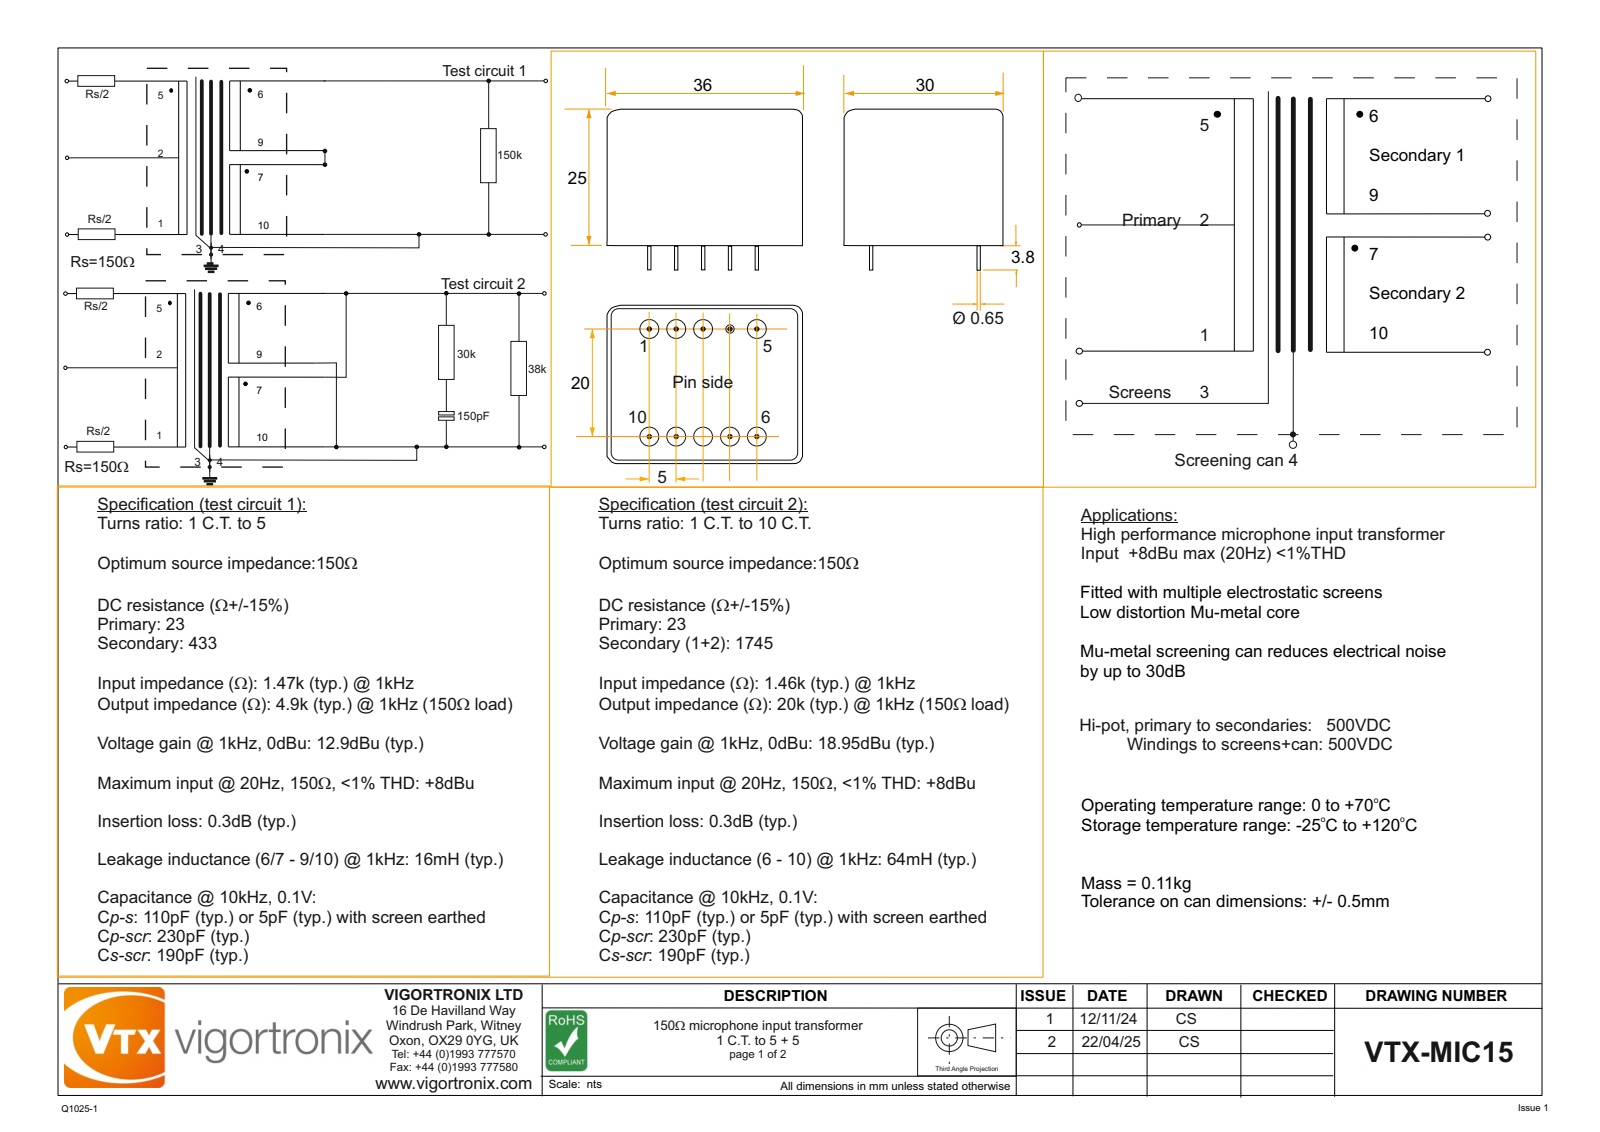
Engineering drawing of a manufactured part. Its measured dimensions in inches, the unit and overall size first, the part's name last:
Units: inches
Overall size (bounding box): 1.417 × 1.181 × 1.134
Round holes (diameter × count): ⌀0.094 ×9, ⌀0.059 ×1
Round bosses / shafts (diameter × count): ⌀0.026 ×9
Partial cylindrical surfaces — rounded edges, fillets, slot ends (radius × count): R0.039 ×8, R0.091 ×8, R0.118 ×8, R0.098 ×4
Main face-to-face distances: 0.028, 0.02, 0.126, 0.106, 0.913, 0.894, 0.787, 0.043, 0.957, 0.937
Hole centre spacings: 0.197, 0.812, 0.787, 0.394, 0.88, 0.591, 0.984, 1.113
Volume: 1.241 in³ · Surface area: 21.64 in²
Bodies: 3 solids, 110 faces (32 planar, 66 cylindrical, 12 other)
Part name (STEP PRODUCT): VTX-MIC15 Can; VTX-MIC15 BOBBIN; VTX-MIC15 Lid; VTX-MIC15
STEP written by: SolidWorks 2024 (AUTOMOTIVE_DESIGN)
